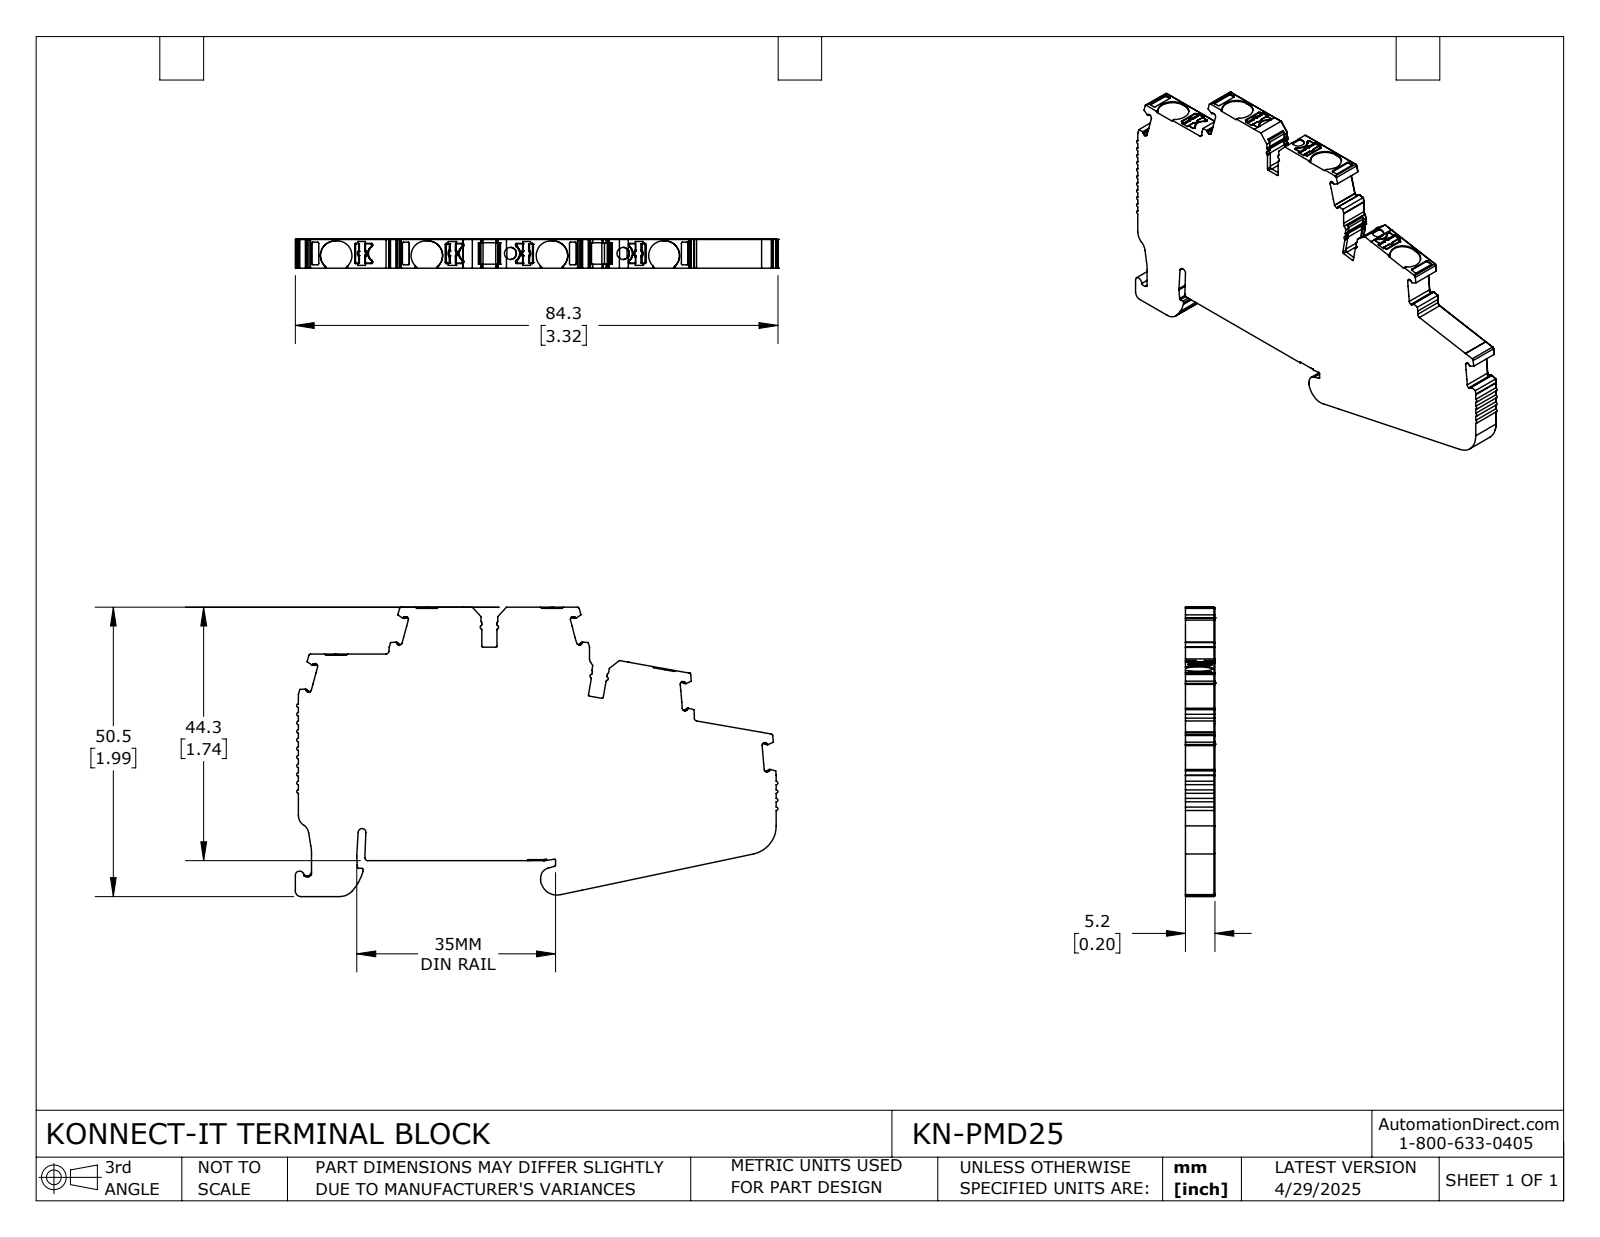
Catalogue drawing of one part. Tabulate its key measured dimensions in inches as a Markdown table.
| quantity | value |
| --- | --- |
| part name | KN-PMD25 |
| STEP written by | SolidWorks 2024 (CONFIG_CONTROL_DESIGN) |
| units | inches |
| bodies | 1 solid, 903 faces (446 planar, 390 cylindrical, 67 other) |
| overall size | 3.318 × 1.989 × 0.203 |
| volume | 0.968 in³ |
| surface area | 12.3 in² |
| round holes (diameter × count) | 0.083 × 2 |
| partial cylindrical surfaces (radius × count) | 0.008 × 85, 0.012 × 47, 0.004 × 31, 0.02 × 21, 0.006 × 16, 0.024 × 12, 0.006 × 10, 0.01 × 10 |
| main face-to-face distances | 0.203, 0.322, 0.322, 0.079, 1.735, 1.412, 1.734, 0.246, 1.981, 0.197 |
